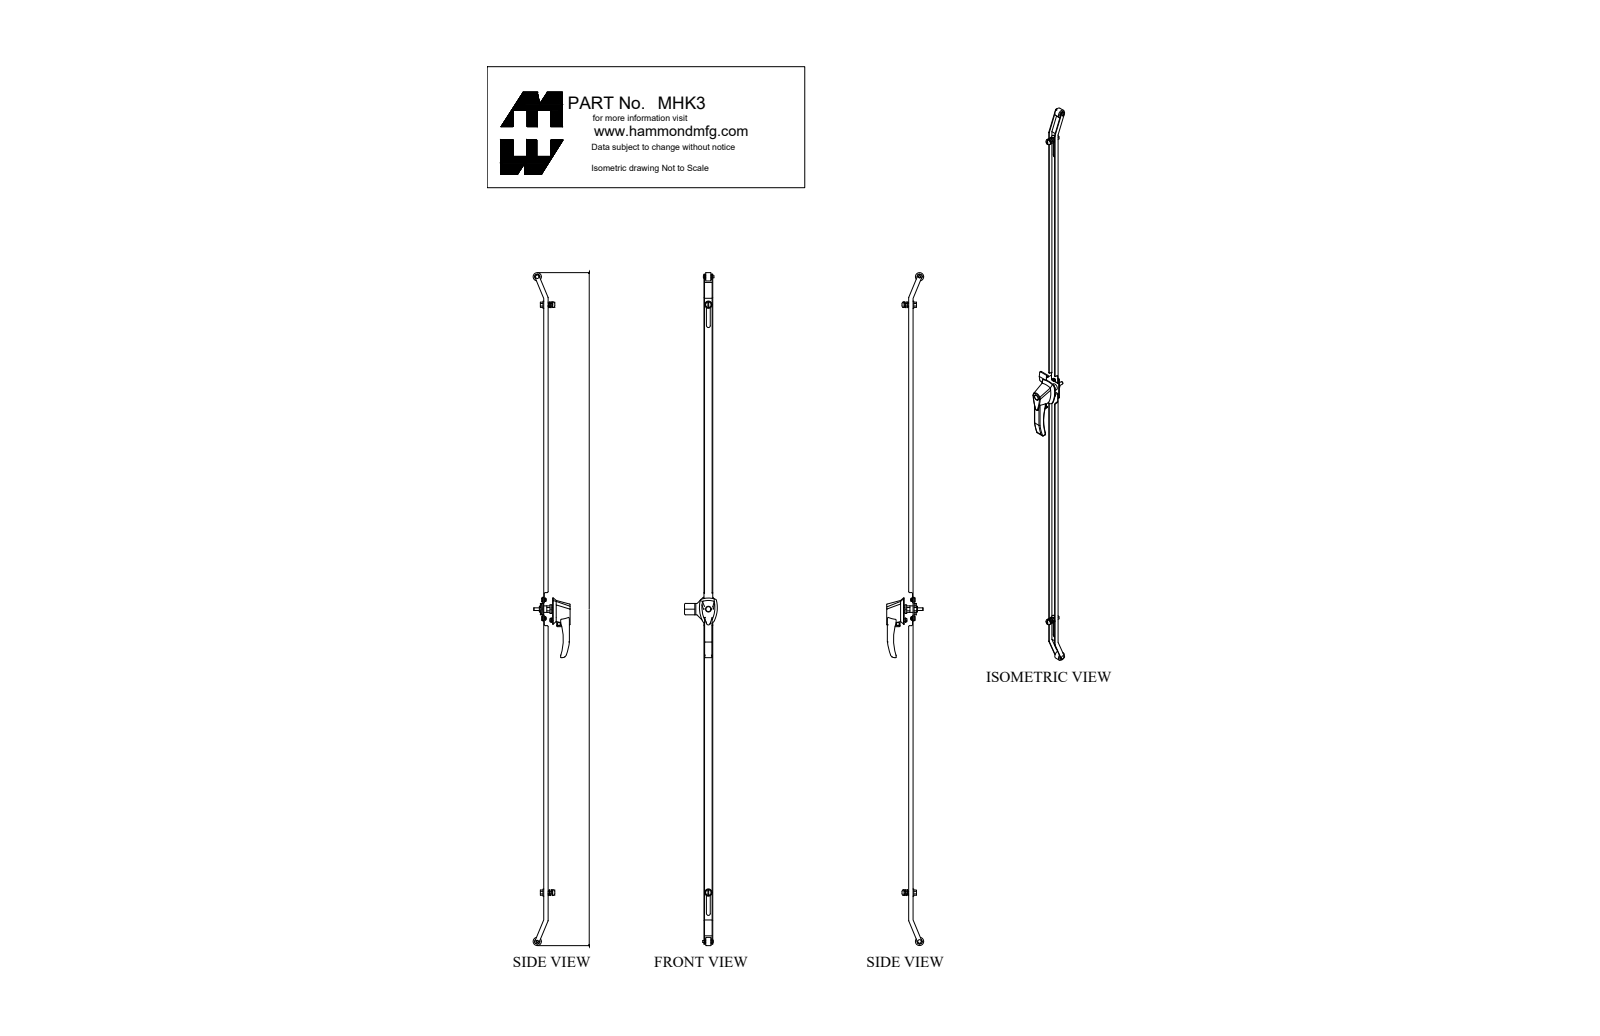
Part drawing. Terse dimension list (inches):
name: MHK3
written by: SolidWorks 2018 (AUTOMOTIVE_DESIGN)
unit: in
bodies: 32 solids, 543 faces (268 planar, 212 cylindrical, 63 other)
size: 81.493 × 4.473 × 3.975
volume: 24.41 in³; area: 416.4 in²
holes: 3× ⌀0.375, 2× ⌀0.159, 2× ⌀0.195, 2× ⌀0.25, 2× ⌀0.257, 2× ⌀0.28, 2× ⌀0.281, 2× ⌀0.307, 2× ⌀0.39, 2× ⌀0.413, 1× ⌀0.173, 1× ⌀0.233
bosses: 3× ⌀0.325, 2× ⌀1, 2× ⌀0.882, 2× ⌀0.678, 2× ⌀0.63, 2× ⌀0.402, 2× ⌀0.278, 2× ⌀0.18
rounds: 22× R0.125, 6× R0.03, 6× R0.06, 6× R0.09, 4× R0.01, 4× R0.234, 2× R0.312, 2× R0.75
face distances: 0.07, 0.992, 1.062, 0.922, 0.531, 0.461, 0.076, 0.986, 0.916, 0.125
hole spacings: 1.126, 1.287, 0.213, 0.625, 1.338, 1.477, 2.251, 2.464
